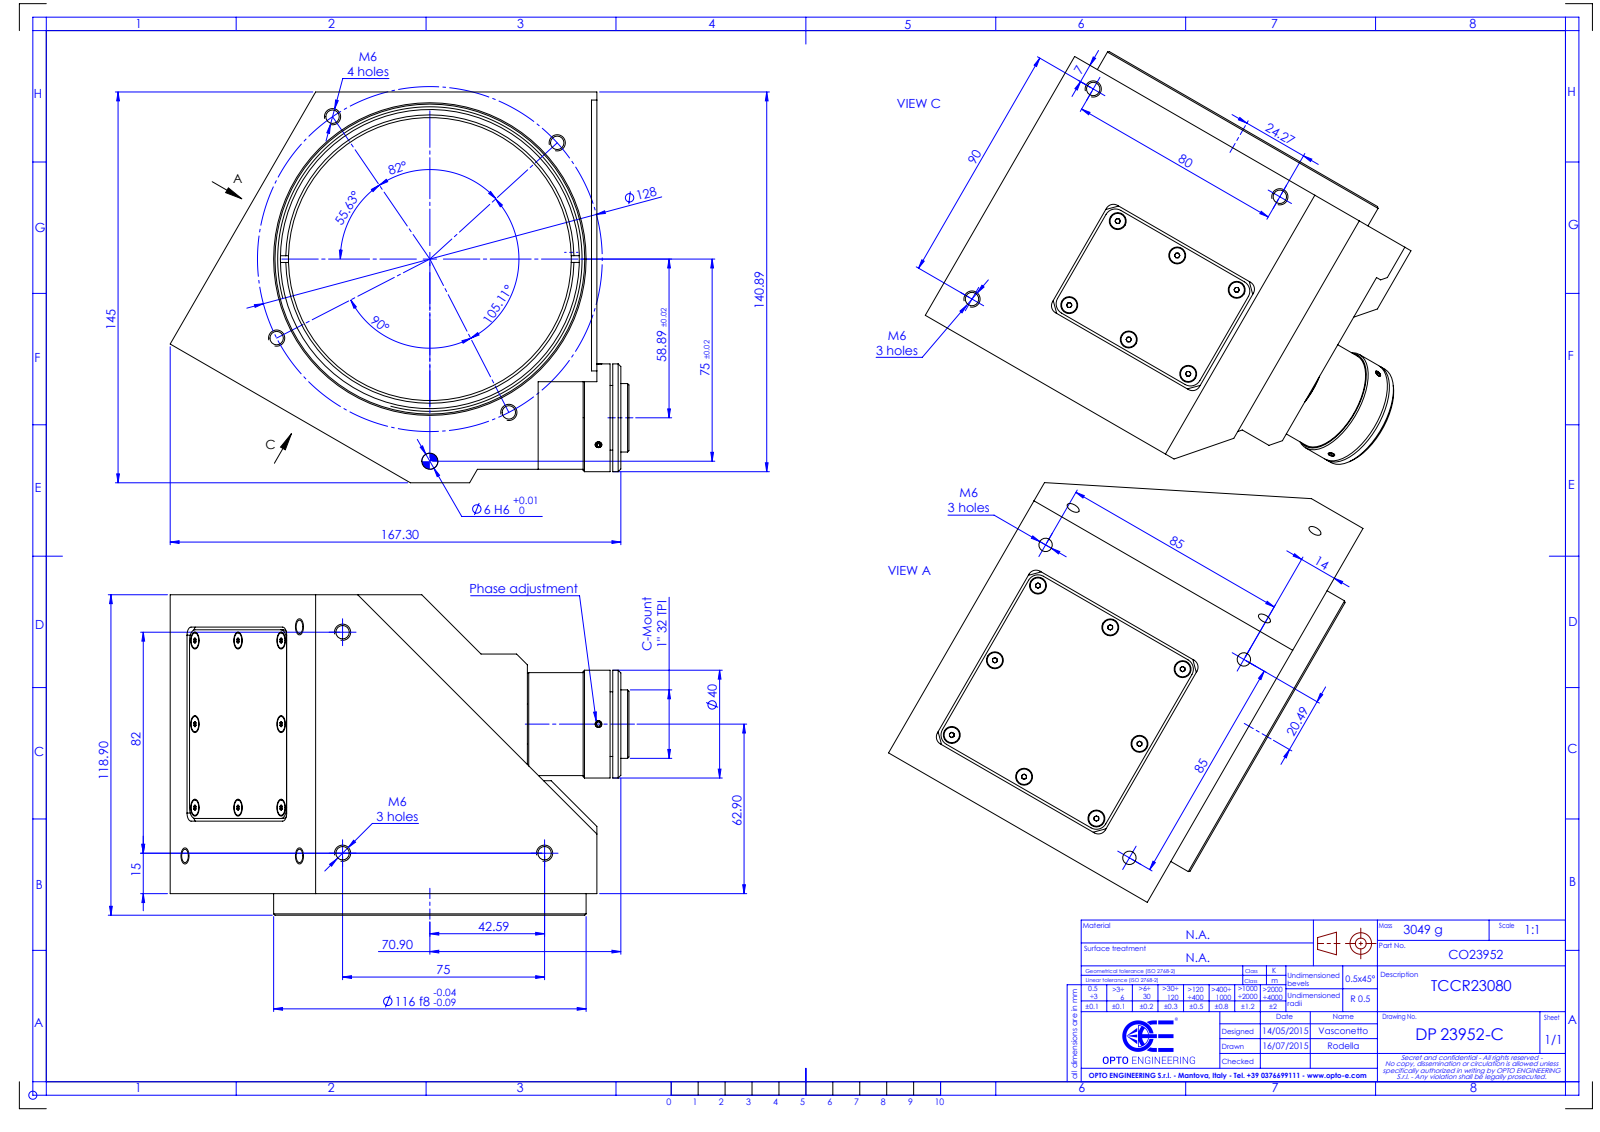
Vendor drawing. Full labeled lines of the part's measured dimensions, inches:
Part name (STEP PRODUCT): DP23952_TCCR23080
STEP written by: SolidWorks 2021 (CONFIG_CONTROL_DESIGN)
Units: inches
Bodies: 0 solids, 325 faces (135 planar, 98 cylindrical, 92 other)
Overall size (bounding box): 6.705 × 5.709 × 4.681
Round holes (diameter × count): ⌀0.197 ×13, ⌀0.236 ×1, ⌀0.866 ×1, ⌀0.886 ×1, ⌀4.134 ×1, ⌀4.37 ×1
Round bosses / shafts (diameter × count): ⌀0.226 ×16, ⌀4.567 ×1, ⌀1.575 ×1, ⌀1.504 ×1, ⌀1.488 ×1, ⌀1 ×1
Partial cylindrical surfaces — rounded edges, fillets, slot ends (radius × count): R0.157 ×10, R0.118 ×8
Main face-to-face distances: 0.02, 4.366, 5.709, 4.075, 1.634, 1.016, 0.157, 5.512, 1.437, 0.197
Hole centre spacings: 2.52, 2.953, 3.346, 1.357, 2.519, 2.872, 3.15, 3.228
